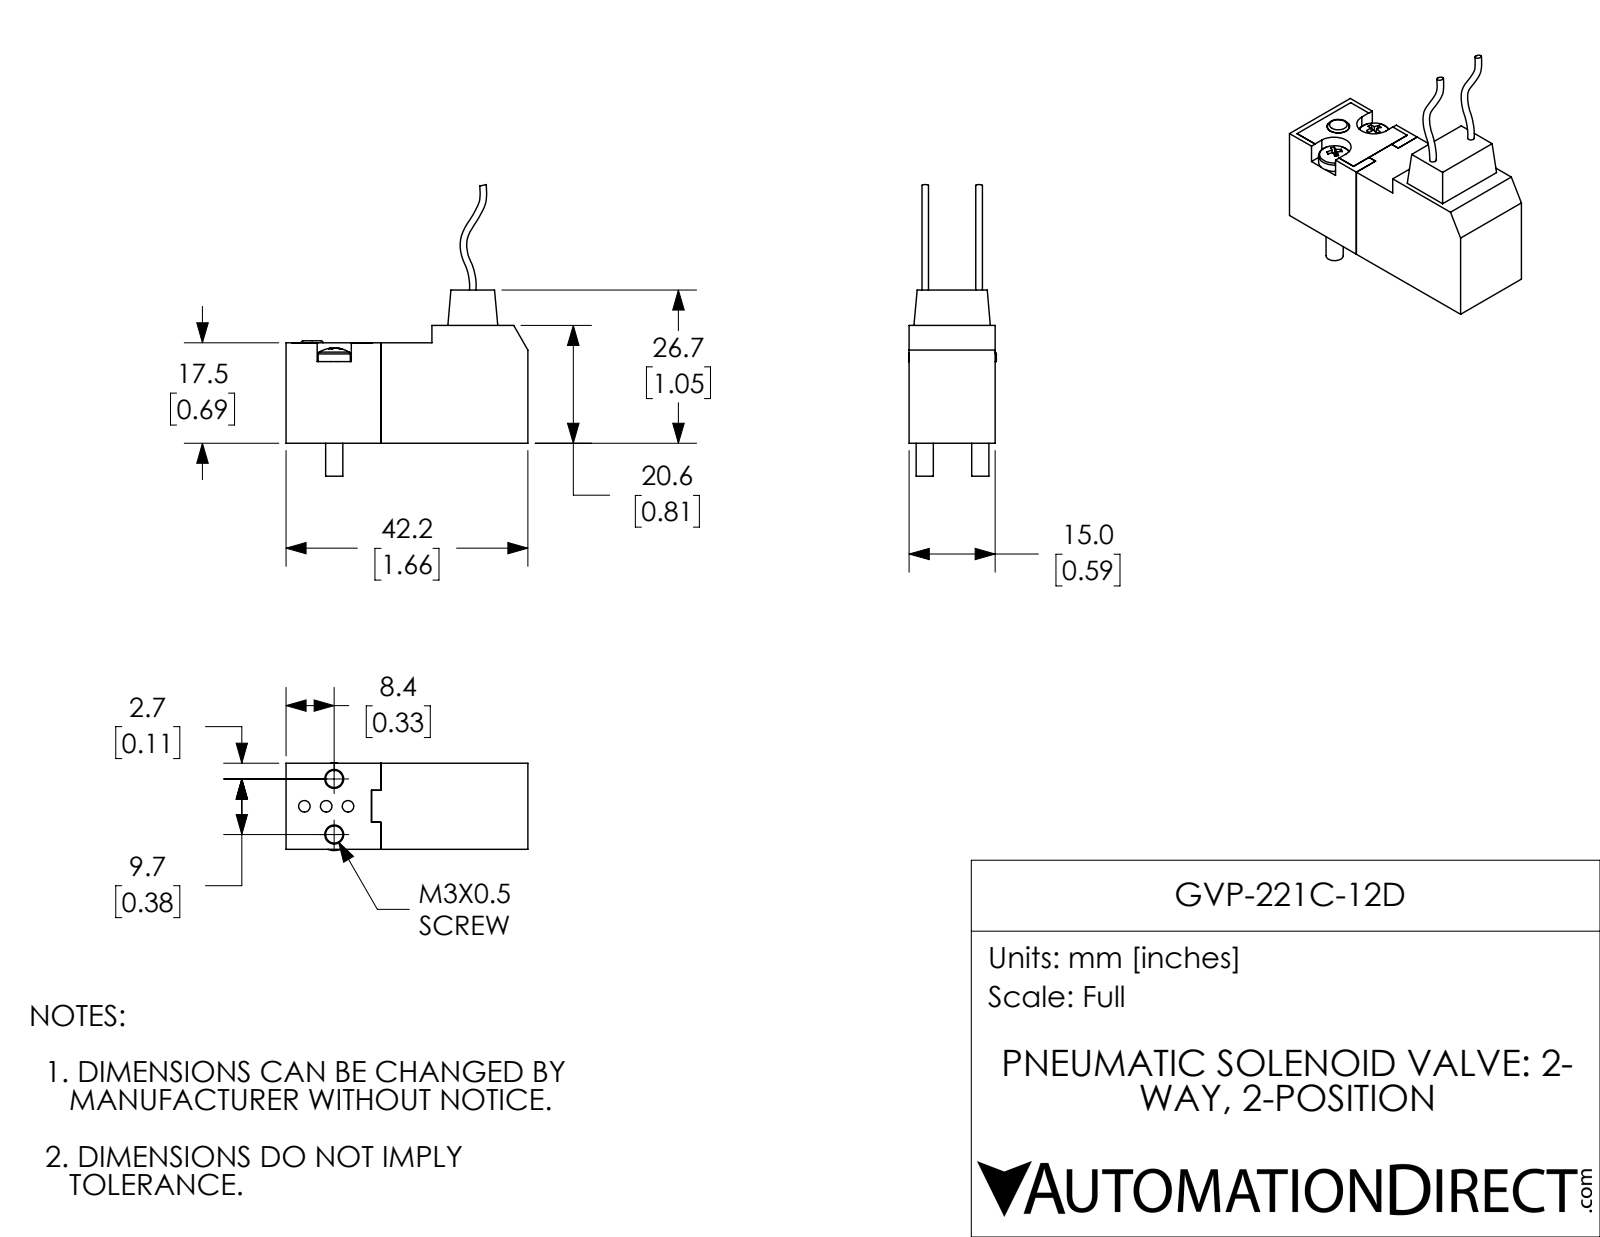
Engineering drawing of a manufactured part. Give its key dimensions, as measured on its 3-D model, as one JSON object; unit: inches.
{"part_name": "GVP-221C-12D", "step_written_by": "SolidWorks 2018 (AUTOMOTIVE_DESIGN)", "units": "inches", "bodies": {"solids": 4, "faces": 116, "planar": 79, "cylindrical": 23, "other": 14}, "overall_size": [2.004, 1.663, 0.602], "volume_in3": 0.755, "surface_area_in2": 8.426, "round_holes": [[0.079, 3], [0.13, 2], [0.155, 1]], "round_bosses_or_shafts": [[0.22, 2], [0.118, 2]], "partial_cylinders_radius": [[0.117, 2]], "face_to_face_distances": [0.591, 0.651, 1.012, 1.663, 1.075, 0.063, 0.588, 0.69, 0.691, 0.186], "hole_center_spacings": [0.15, 0.053, 0.097, 0.196, 0.202, 0.211, 0.216, 0.242]}
